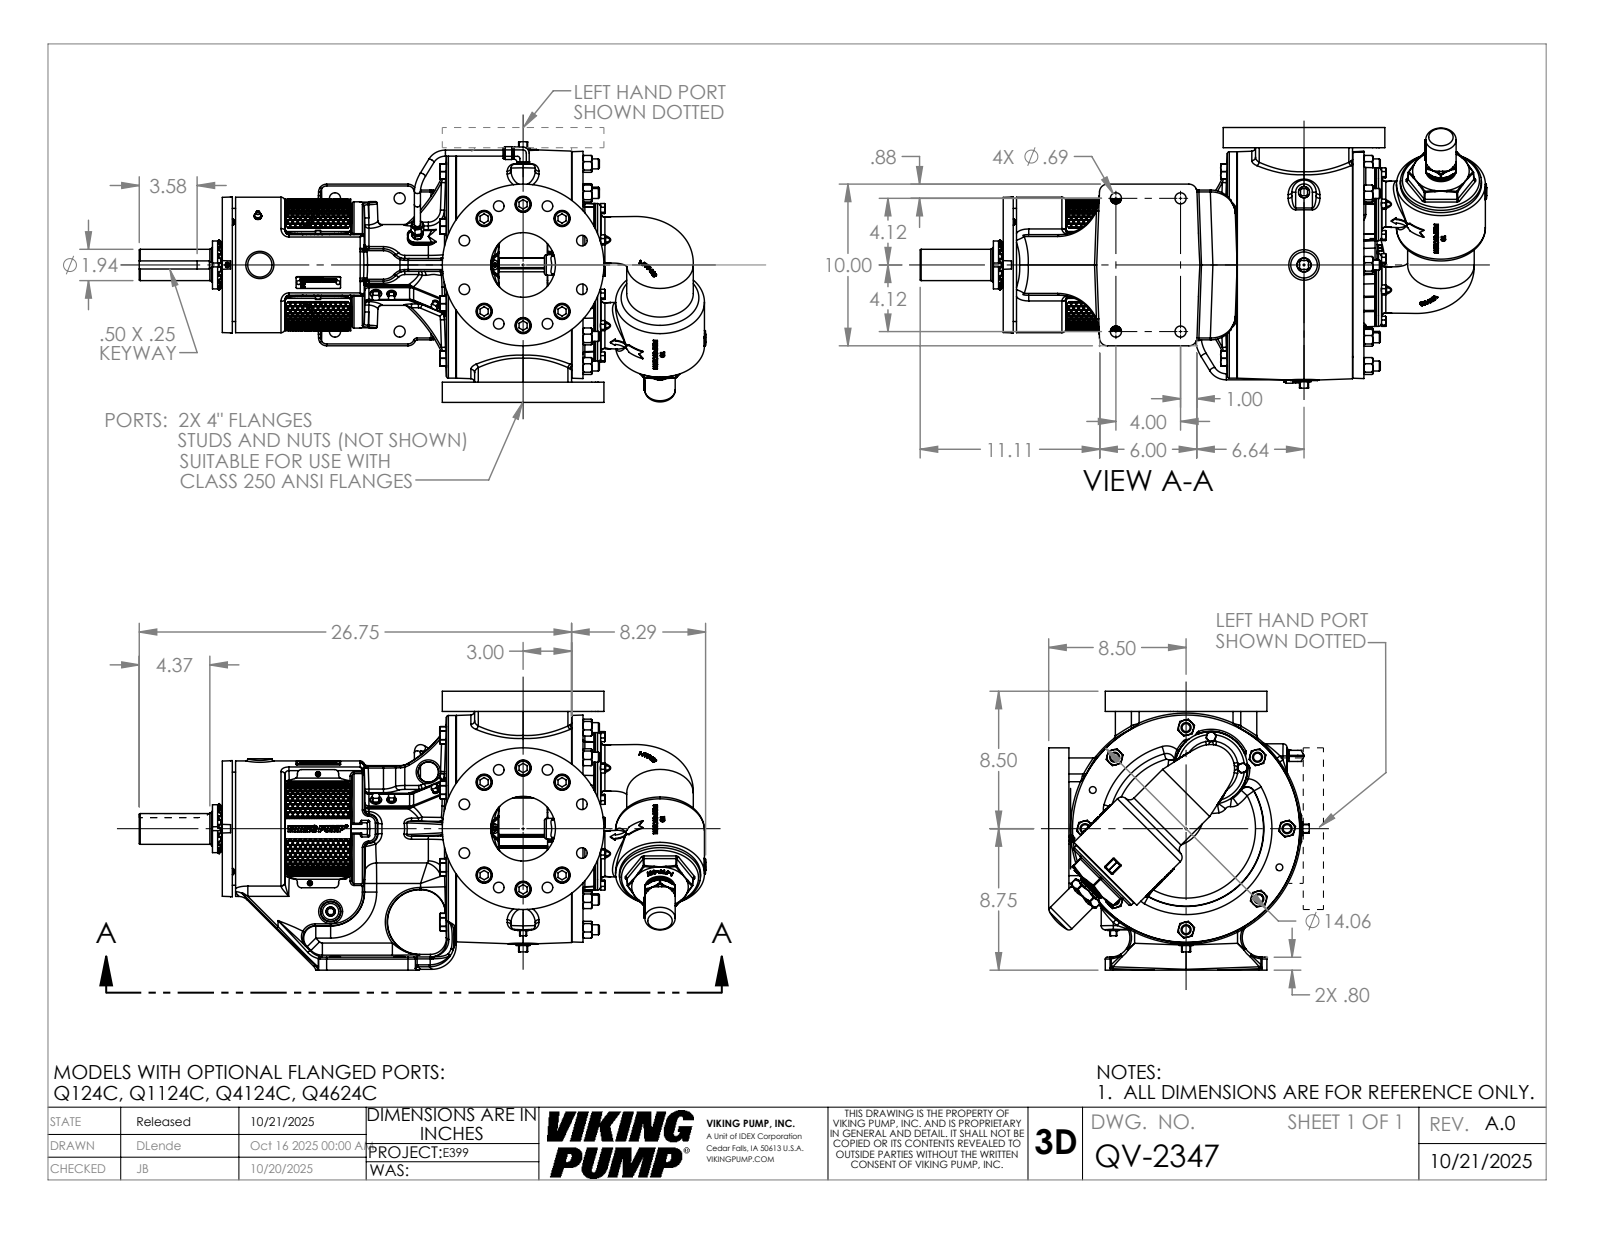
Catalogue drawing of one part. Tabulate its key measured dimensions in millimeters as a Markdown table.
| quantity | value |
| --- | --- |
| part name | QV-2347 |
| STEP written by | SolidWorks 2024 (AUTOMOTIVE_DESIGN) |
| units | millimeters |
| bodies | 1 solid, 4977 faces (1685 planar, 845 cylindrical, 2447 other) |
| overall size | 890.1 × 438.2 × 412 |
| volume | 38 080 000 mm³ |
| surface area | 1 578 000 mm² |
| round holes (diameter × count) | 16.7 × 16, 25.4 × 12, 6.4 × 9, 6.8 × 8, 10.3 × 8, 10.4 × 8, 29.4 × 8, 17.5 × 4, 4 × 2, 8 × 2, 10.7 × 2, 101.6 × 2 |
| round bosses / shafts (diameter × count) | 23.8 × 12, 9.5 × 10, 15.7 × 8, 9.5 × 4, 7.9 × 3, 4.8 × 3, 254 × 2, 114.3 × 2 |
| partial cylindrical surfaces (radius × count) | 3 × 66, 6.4 × 22, 1.5 × 20, 0.4 × 18, 2.3 × 18, 1.8 × 16, 19.1 × 16, 0.8 × 13 |
| main face-to-face distances | 31.8, 438.2, 566.9, 406.4, 97, 469.8, 202.5, 105.5, 364.4, 3 |
| hole center spacings | 95.3, 184.8, 52.8, 100, 146.9, 30.1, 68.9, 76.5 |
